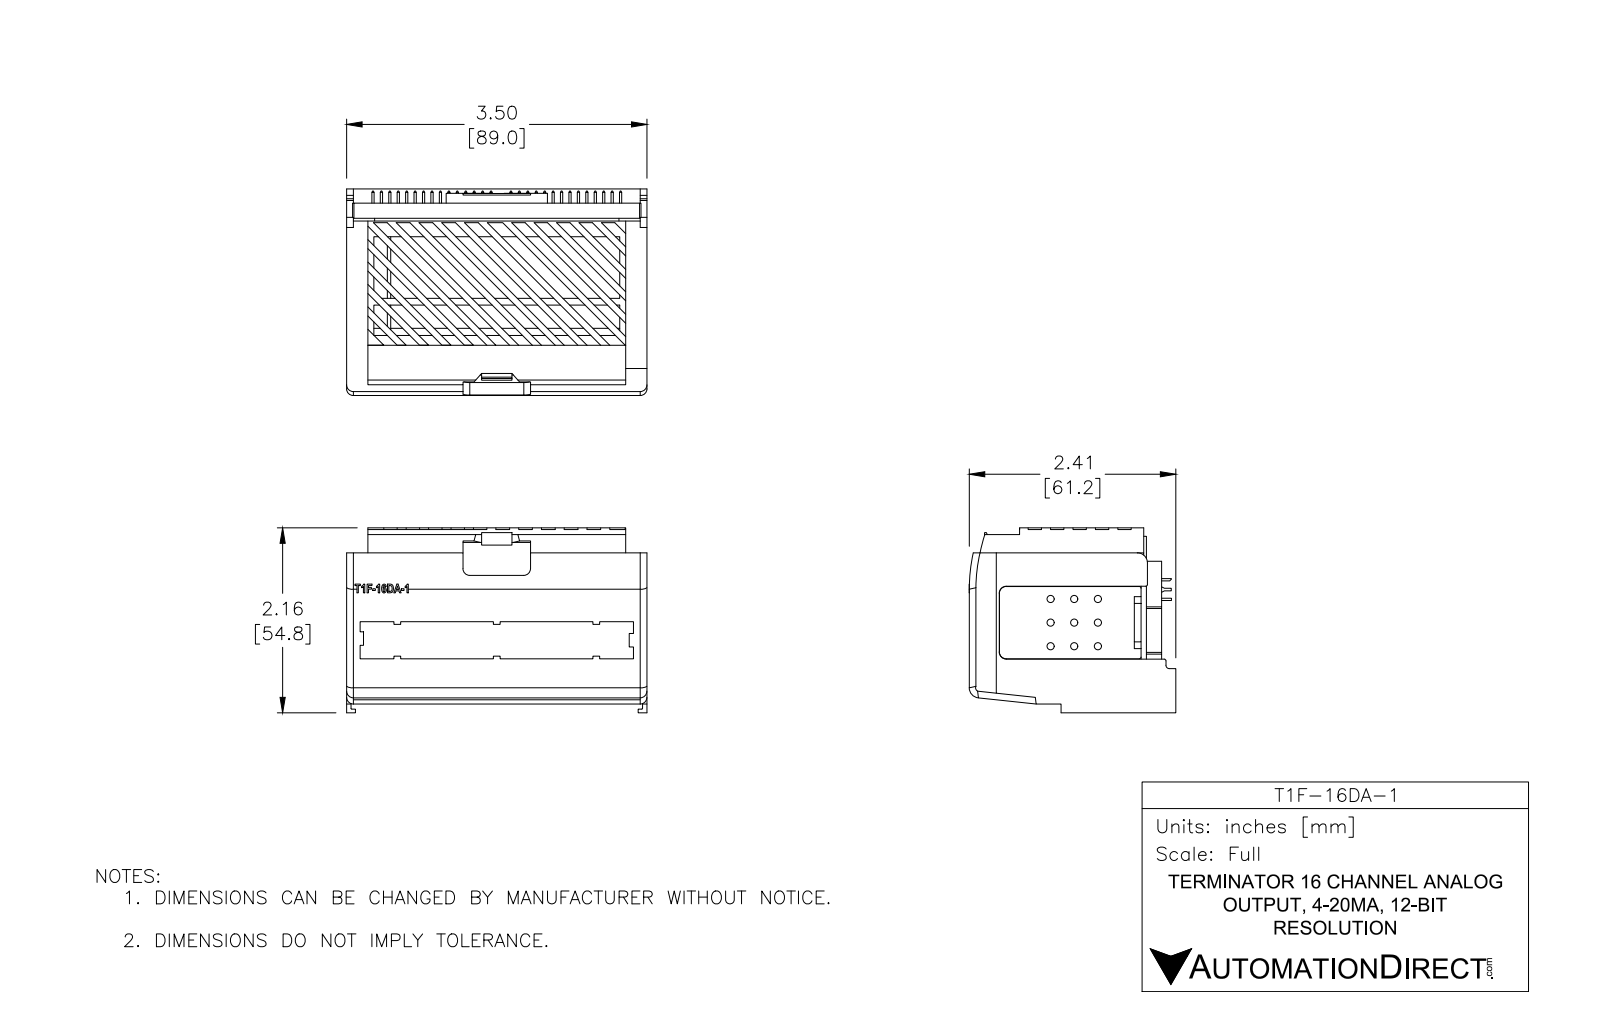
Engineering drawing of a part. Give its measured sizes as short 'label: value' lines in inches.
name: T1F-16DA-1
written by: SolidWorks 2013 (AUTOMOTIVE_DESIGN)
unit: in
bodies: 1 solid, 646 faces (450 planar, 181 cylindrical, 15 other)
size: 3.492 × 2.563 × 2.416
volume: 2.774 in³; area: 84.51 in²
holes: 16× ⌀0.118
bosses: 56× ⌀0.028
rounds: 18× R0.138, 5× R0.039, 3× R0.01, 3× R0.022, 2× R0.059, 1× R0.315, 1× R0.394, 1× R0.709
face distances: 0.079, 3.413, 2.179, 0.02, 2.354, 3.492, 0.059, 2.176, 2.1, 3.335
hole spacings: 0.203, 0.406, 0.608, 0.811, 1.014, 1.217, 1.419, 1.622
